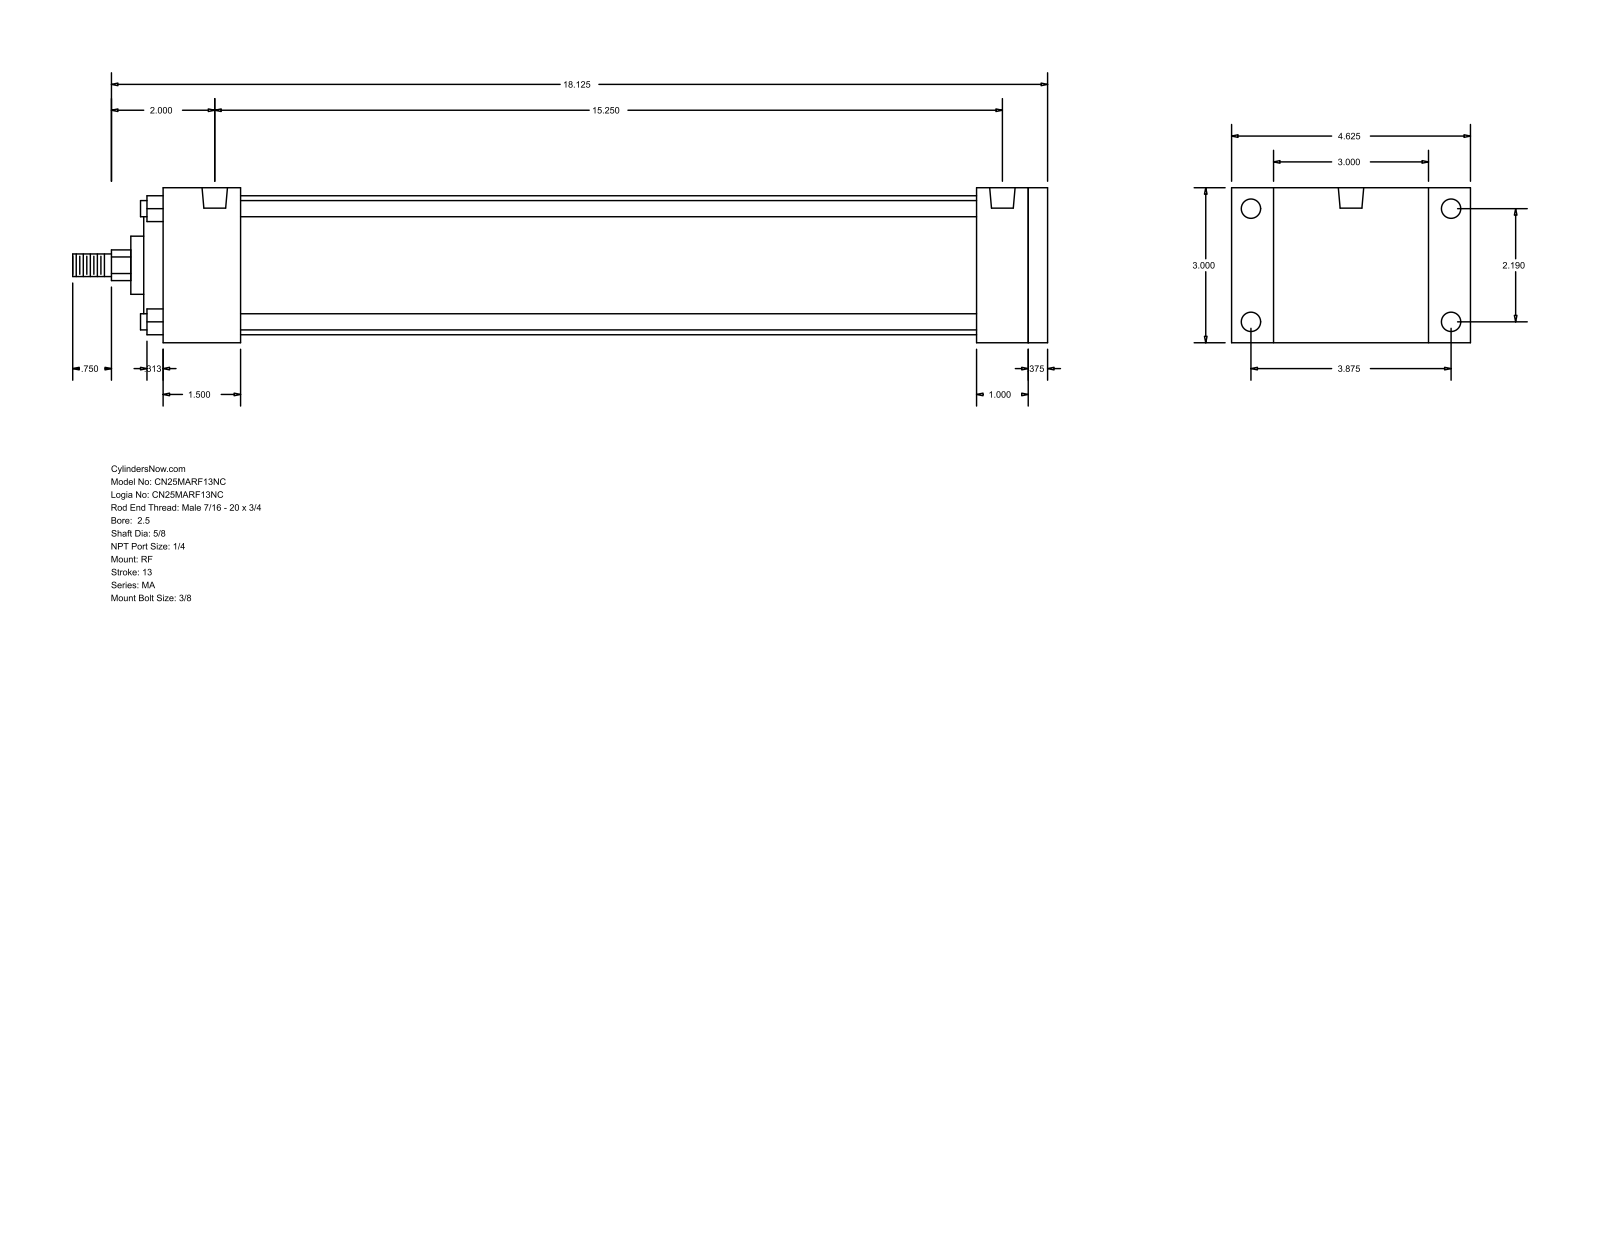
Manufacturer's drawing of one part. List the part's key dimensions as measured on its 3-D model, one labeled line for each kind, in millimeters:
Part name (STEP PRODUCT): MA_RF__0250_0.625
STEP written by: GSSL Pune (CONFIG_CONTROL_DESIGN)
Units: millimetres
Bodies: 0 solids, 94 faces (65 planar, 29 cylindrical, 0 other)
Overall size (bounding box): 479.43 × 117.47 × 76.2
Round holes (diameter × count): ⌀7.94 ×4, ⌀9.53 ×4, ⌀12.49 ×2
Round bosses / shafts (diameter × count): ⌀7.94 ×4, ⌀68.33 ×1, ⌀50.8 ×1, ⌀28.57 ×1, ⌀15.88 ×1, ⌀11.11 ×1
Partial cylindrical surfaces — rounded edges, fillets, slot ends (radius × count): R7.54 ×1
Main face-to-face distances: 76.2, 434.98, 9.53, 425.45, 25.4, 34.93, 38.1, 400.05, 361.95, 387.35
Hole centre spacings: 55.62, 98.42, 113.05, 387.35
